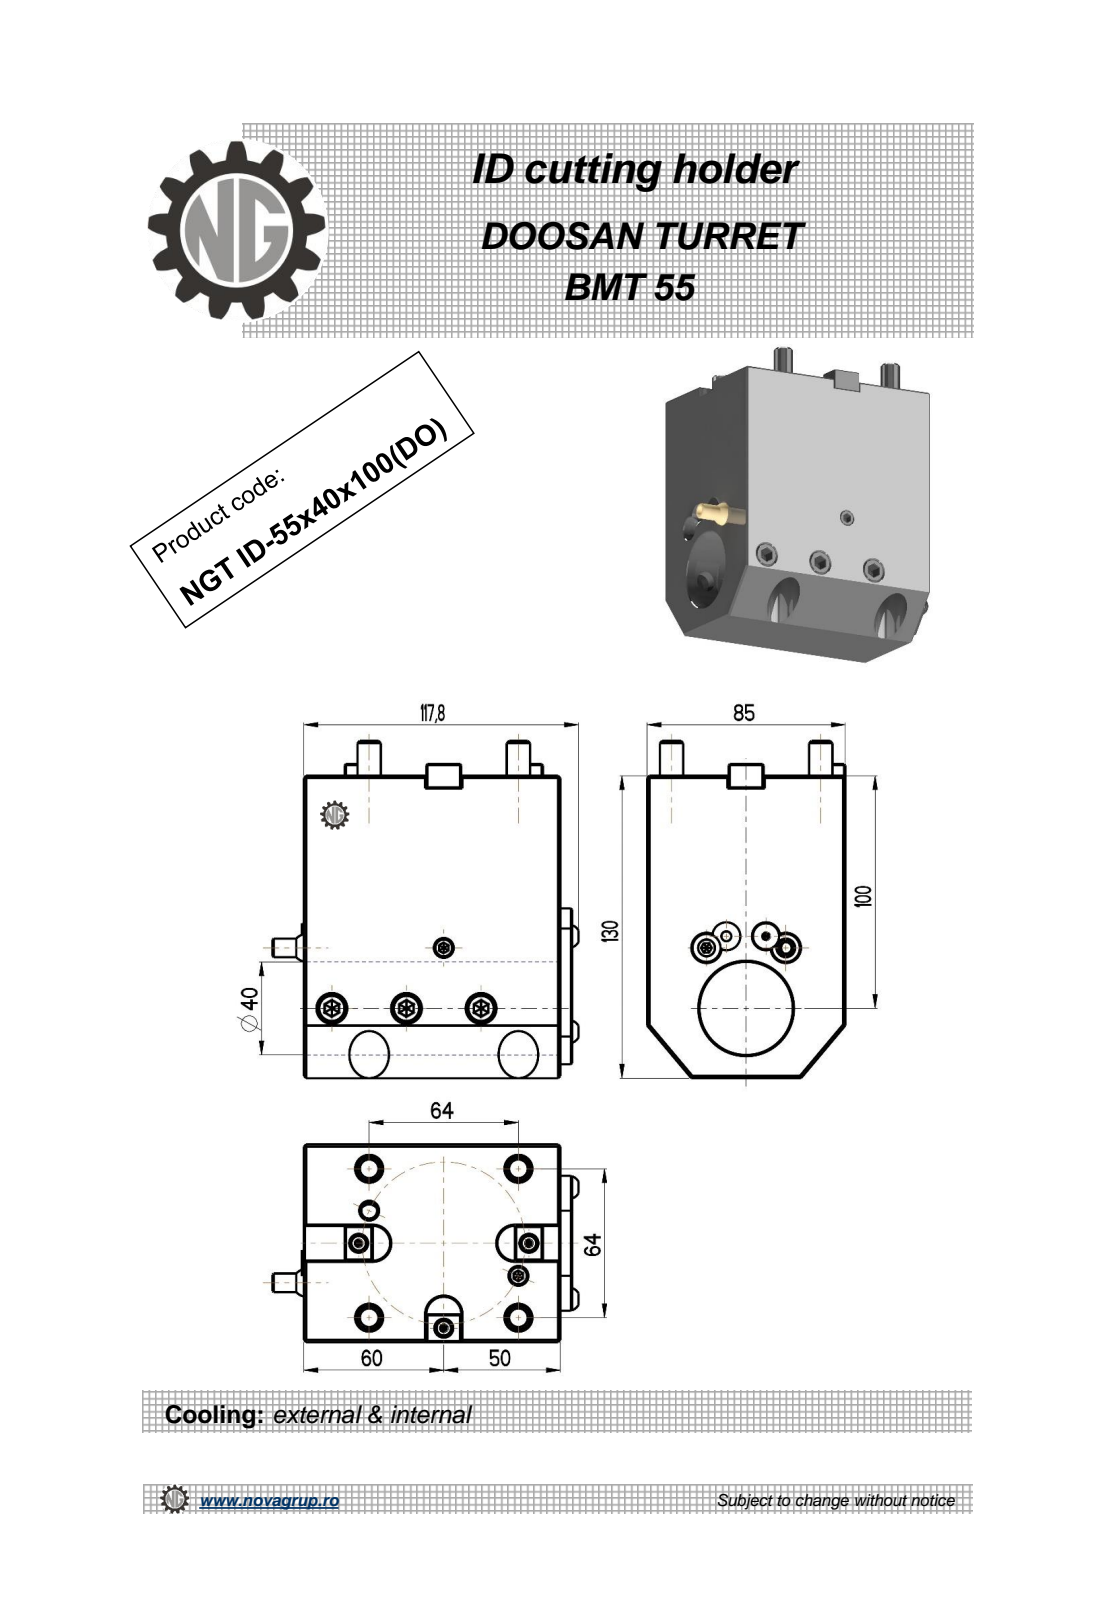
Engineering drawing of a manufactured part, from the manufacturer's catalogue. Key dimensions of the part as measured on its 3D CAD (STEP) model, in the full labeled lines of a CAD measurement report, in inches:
Part name (STEP PRODUCT): NGT_ID_55_40_100_DO
STEP written by: PRO/ENGINEER BY PARAMETRIC TECHNOLOGY CORPORATION, 2010280 (CONFIG_CONTROL_DESIGN)
Units: inches
Bodies: 1 solid, 390 faces (212 planar, 80 cylindrical, 98 other)
Overall size (bounding box): 5.709 × 5.165 × 3.346
Volume: 63.77 in³ · Surface area: 137 in²
Round holes (diameter × count): ⌀0.402 ×3, ⌀0.197 ×1, ⌀0.268 ×1, ⌀1.575 ×1
Round bosses / shafts (diameter × count): ⌀0.394 ×4, ⌀0.441 ×1, ⌀0.315 ×1
Partial cylindrical surfaces — rounded edges, fillets, slot ends (radius × count): R0.024 ×36, R0.009 ×6, R0.016 ×6, R0.295 ×3
Main face-to-face distances: 3.346, 4.331, 5.118, 0.197, 4.528, 0.63, 1.378, 4.921, 0.394, 1.969
Hole centre spacings: 1.26, 1.223, 2.52
